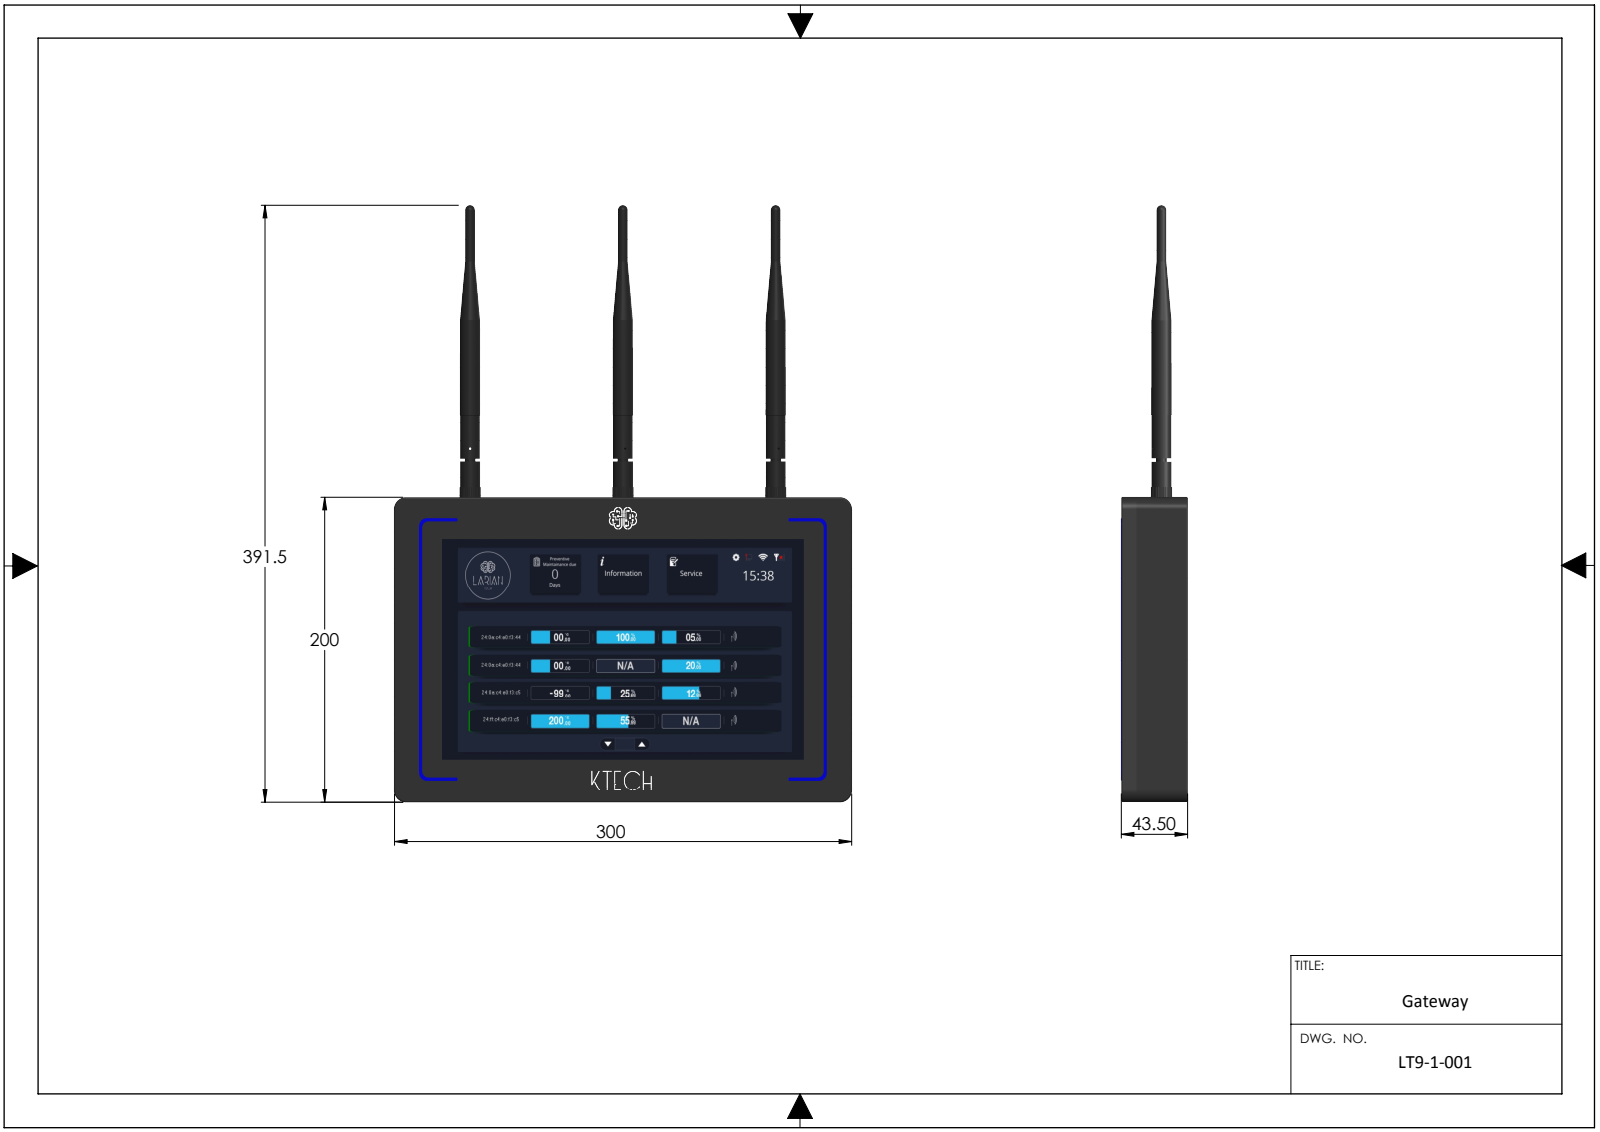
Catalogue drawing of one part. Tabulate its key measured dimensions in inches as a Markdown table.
| quantity | value |
| --- | --- |
| part name | LT9-1-001 Gateway |
| STEP written by | SolidWorks 2020 (AUTOMOTIVE_DESIGN) |
| units | inches |
| bodies | 0 solids, 1949 faces (697 planar, 696 cylindrical, 556 other) |
| overall size | 15.414 × 11.811 × 1.713 |
| round holes (diameter × count) | 0.098 × 12, 0.063 × 4, 0.134 × 4, 0.056 × 3, 0.256 × 3, 0.878 × 1 |
| round bosses / shafts (diameter × count) | 0.236 × 8, 0.197 × 4, 0.516 × 3, 0.51 × 3, 0.279 × 3, 0.253 × 3, 0.1 × 1 |
| partial cylindrical surfaces (radius × count) | 0.007 × 16, 0.02 × 8, 0.039 × 8, 0.059 × 8, 0.098 × 8, 0.007 × 4, 0.079 × 4, 0.157 × 4 |
| main face-to-face distances | 0.118, 1.594, 1.476, 0.1, 1.376, 1.494, 0.218, 1.713, 7.756, 0.059 |
| hole center spacings | 1.033, 2.454, 3.429, 3.937, 5.132, 6.136, 6.554, 7.786 |
